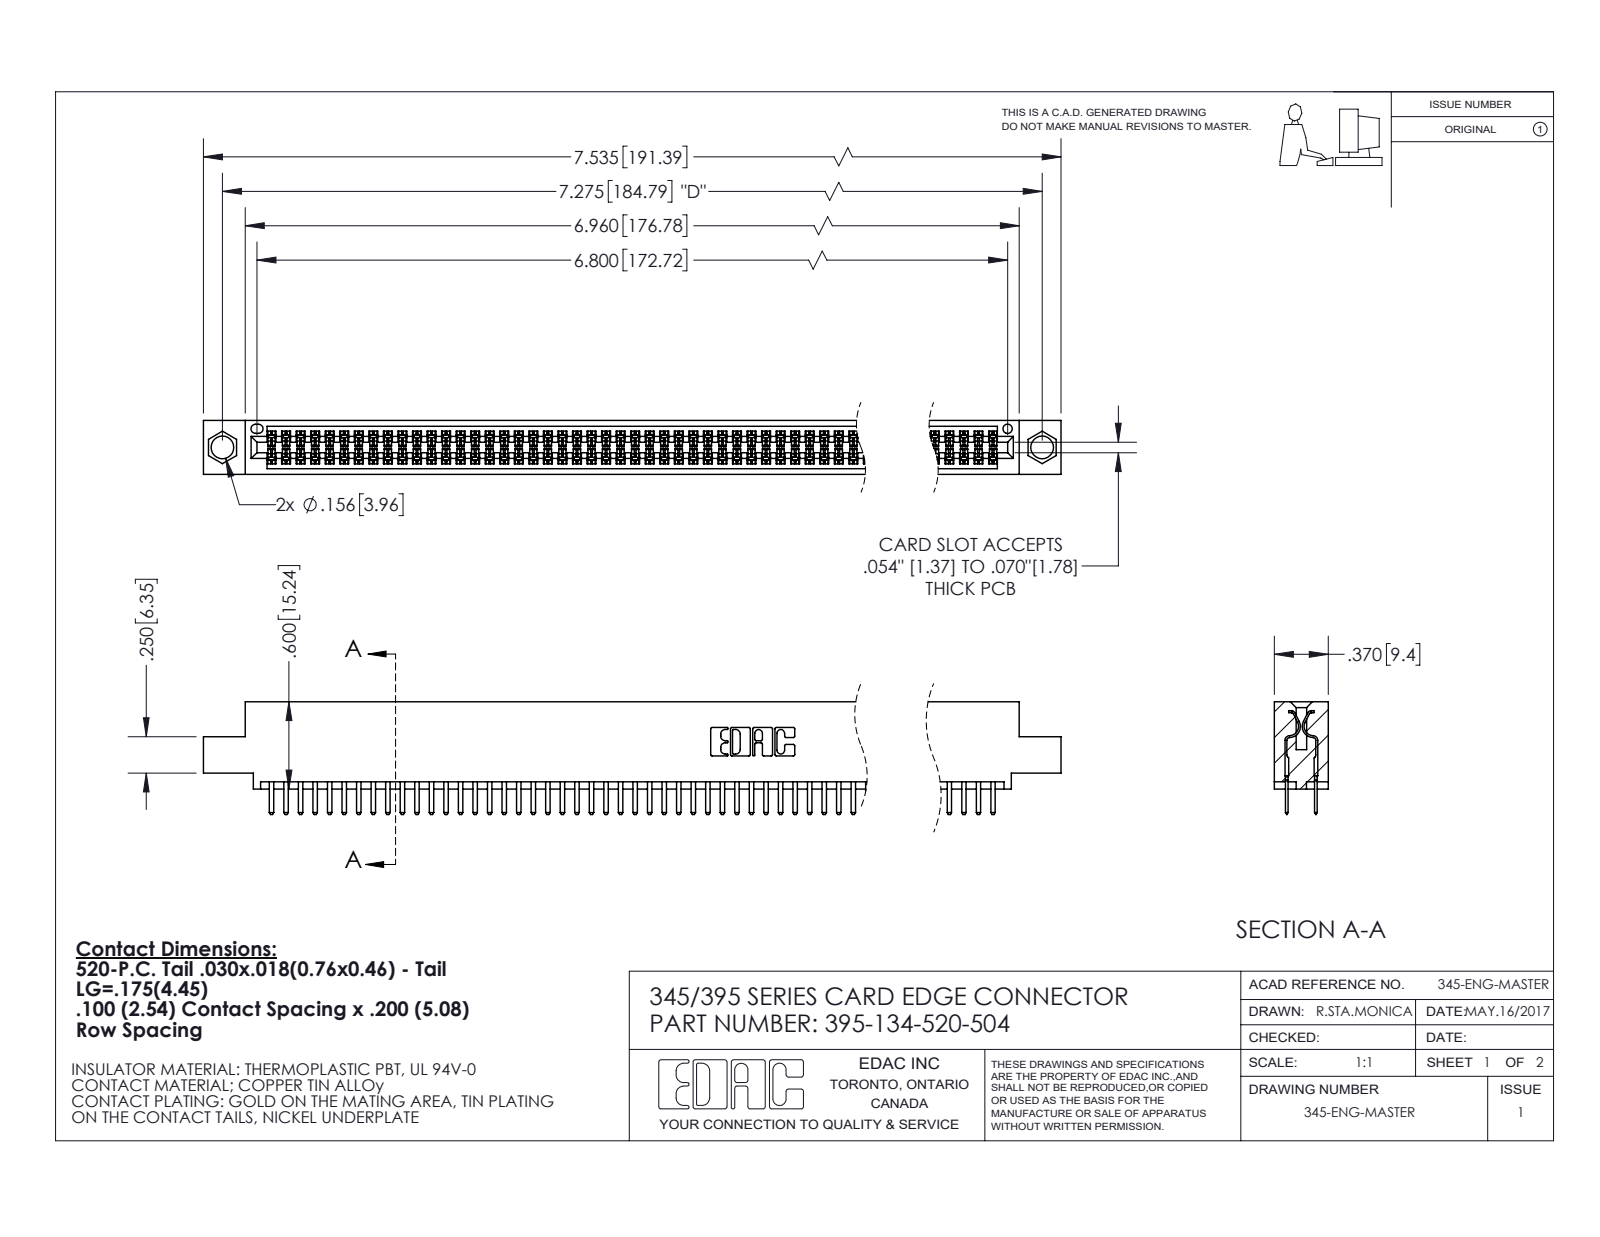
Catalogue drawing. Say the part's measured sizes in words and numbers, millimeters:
The part is named "345 Part_0.110 Offset - 0.156 Dia-TI; 345-292-001_345-293-120; 395-134-520-504". Its 3-D file was written by "SolidWorks 2020 (CONFIG_CONTROL_DESIGN)". It is 135 solids with 7380 faces: 4788 planar, 2592 cylindrical and 0 other. Overall it measures 191.4 by 19.7 by 9.4 millimeters. Its volume is 18 580 cubic millimeters and its surface area 27 770 square millimeters. Round holes: 2 of diameter 4, 1 of diameter 1.6. Partial cylindrical surfaces (rounded edges, fillets, slot ends): 201 of radius 0.2, 138 of radius 0.3, 22 of radius 0.3, 6 of radius 0.2, 6 of radius 0.8, 3 of radius 0.7, 2 of radius 0.4, 2 of radius 0.5. The main face-to-face distances are 1.8, 7.6, 5.1, 9.4, 2.5, 6.9, 0.6, 5.7, 0.6, 1.8. The hole center spacings are 6.9, 178.8, 184.8.
